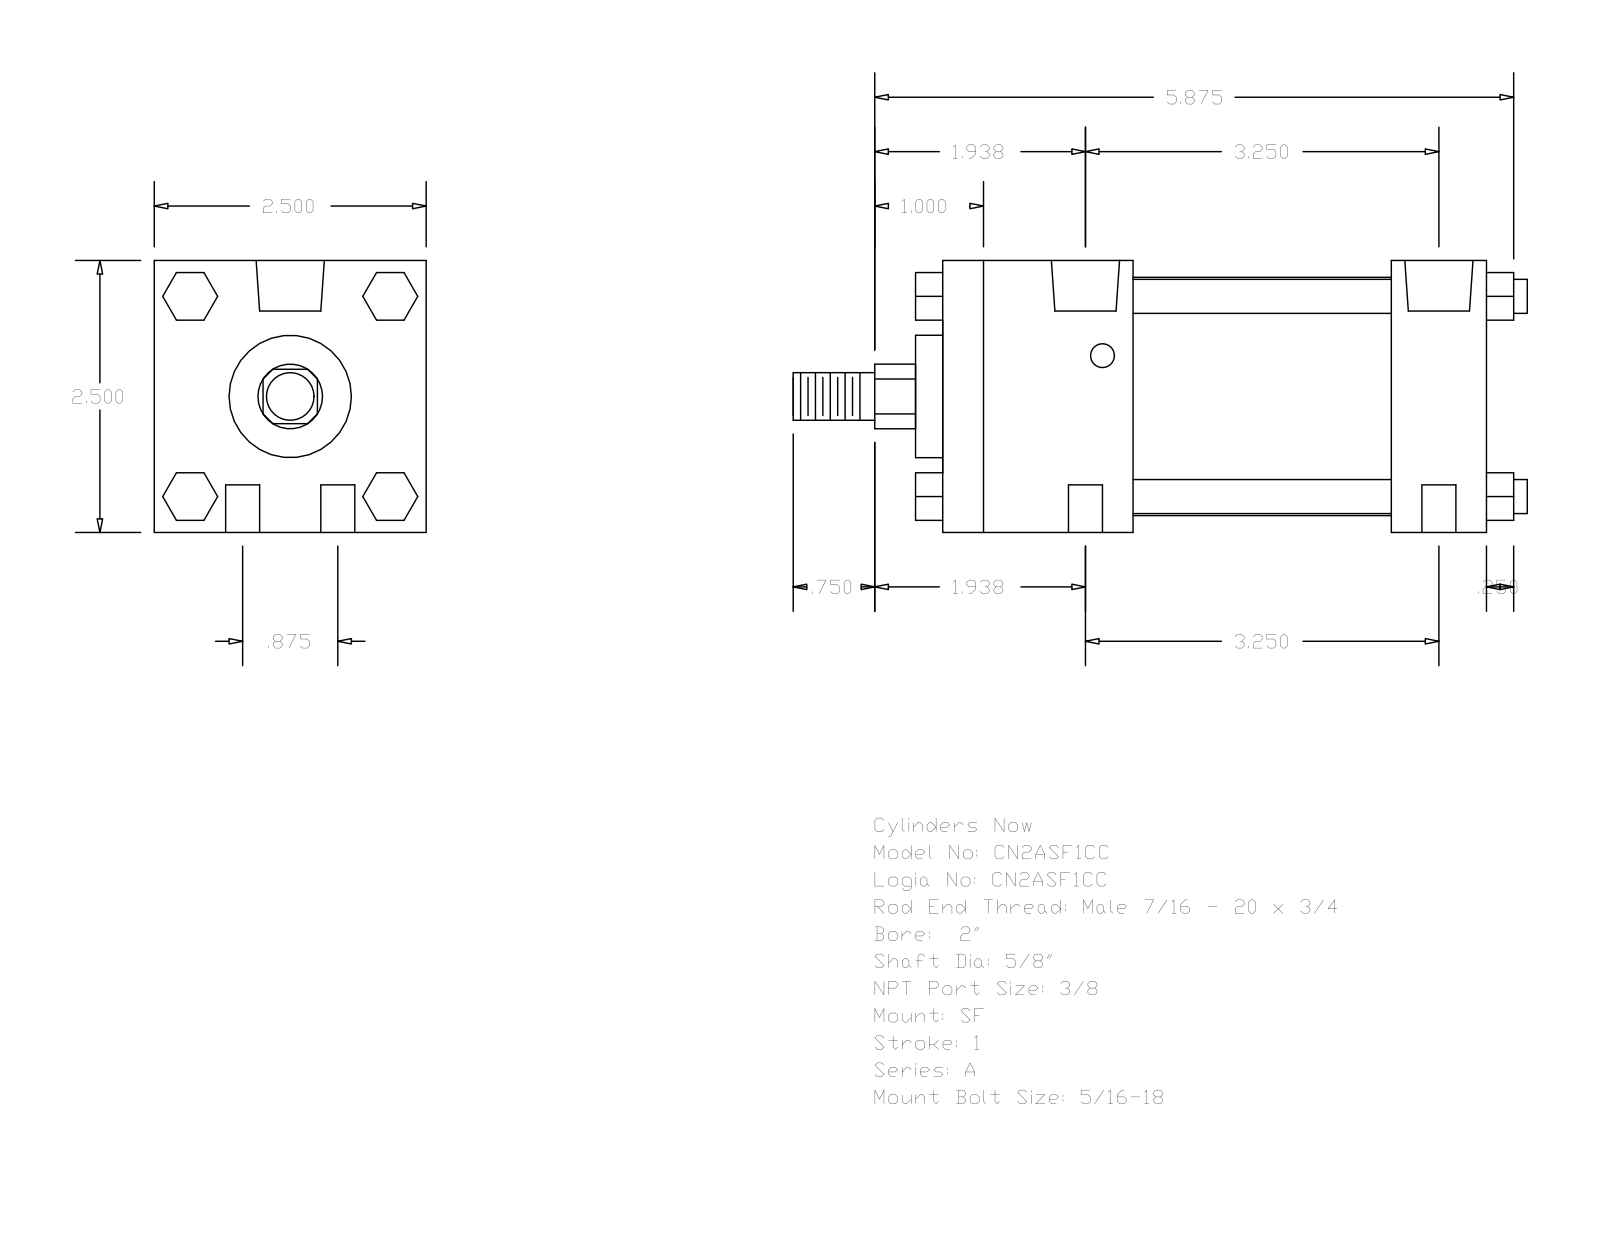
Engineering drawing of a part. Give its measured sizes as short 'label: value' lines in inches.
name: A_SF__0200_0.625
written by: GSSL Pune (CONFIG_CONTROL_DESIGN)
unit: in
bodies: 0 solids, 124 faces (94 planar, 30 cylindrical, 0 other)
size: 6.75 × 2.5 × 2.5
holes: 4× ⌀0.313, 2× ⌀0.219, 2× ⌀0.627
bosses: 4× ⌀0.313, 1× ⌀2.19, 1× ⌀1.125, 1× ⌀0.625, 1× ⌀0.437
rounds: 1× R0.297
face distances: 2.5, 5, 4.125, 0.875, 1.75, 2.375, 3.25, 2, 0.25, 4.375
hole spacings: 0.437, 3.279, 3.25, 0.875, 3.366, 2.937
